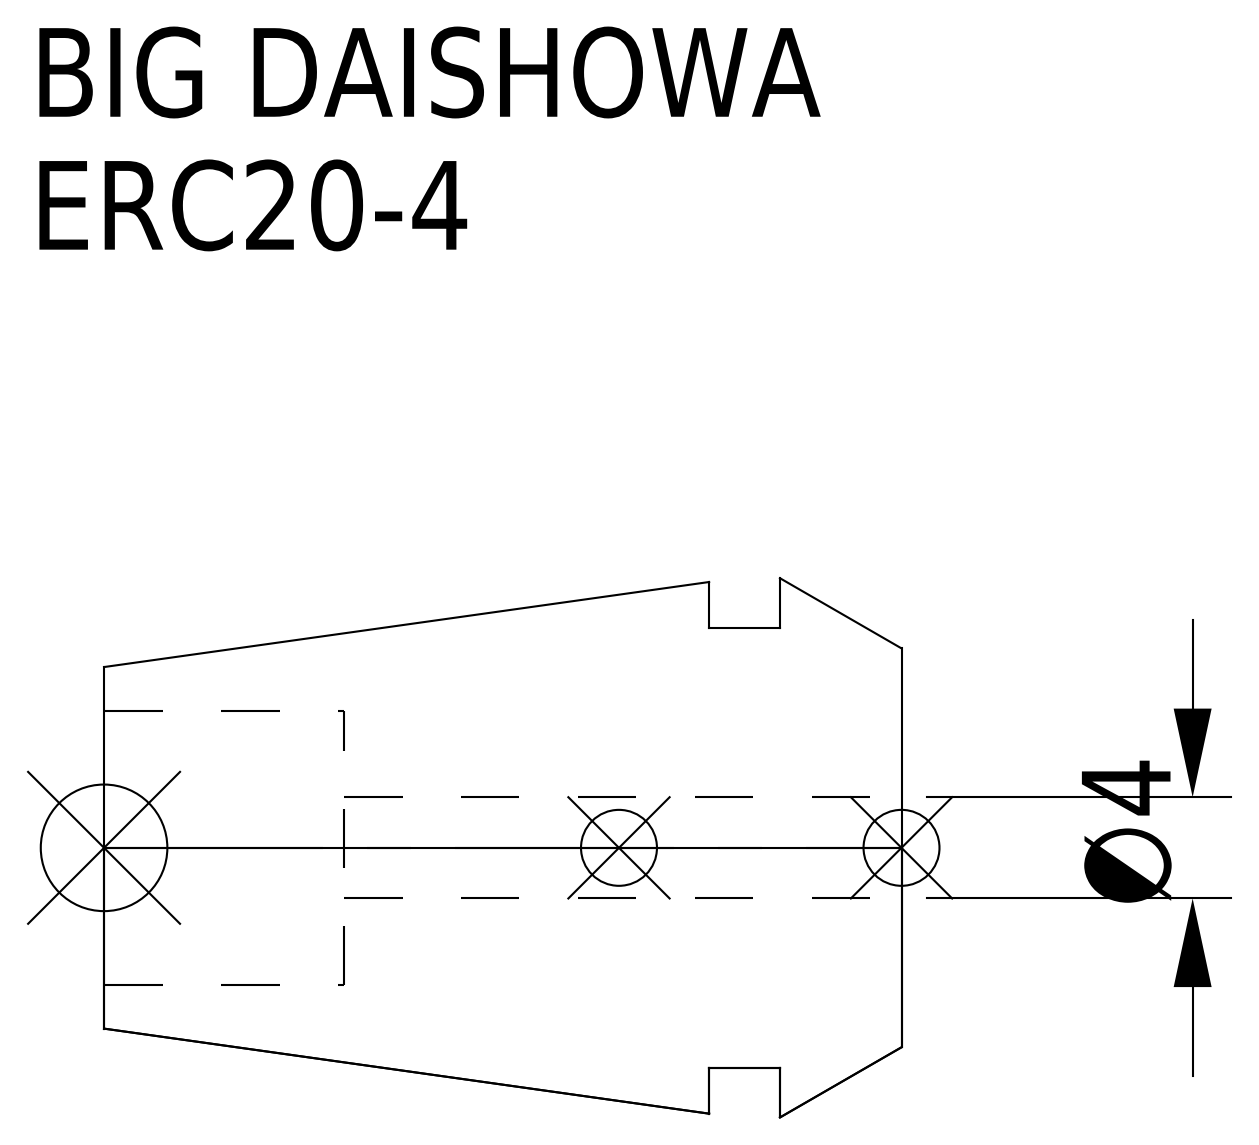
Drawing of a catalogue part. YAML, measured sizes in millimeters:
part_name: "ERC20-4"
step_written_by: "CREO PARAMETRIC BY PTC INC, 2016380 (AUTOMOTIVE_DESIGN)"
units: millimeters
bodies: {solids: 1, faces: 15, planar: 5, cylindrical: 6, other: 4}
overall_size: [31.5, 21.3, 21.3]
volume: 6737
surface_area: 2969
round_holes:
  - {diameter: 4, count: 1}
  - {diameter: 10.8, count: 1}
round_bosses_or_shafts:
  - {diameter: 17.4, count: 1}
face_to_face_distances: [4.8, 7.6, 2.8, 22.02, 17.22, 14.42, 31.5, 26.7, 23.9, 9.48]
